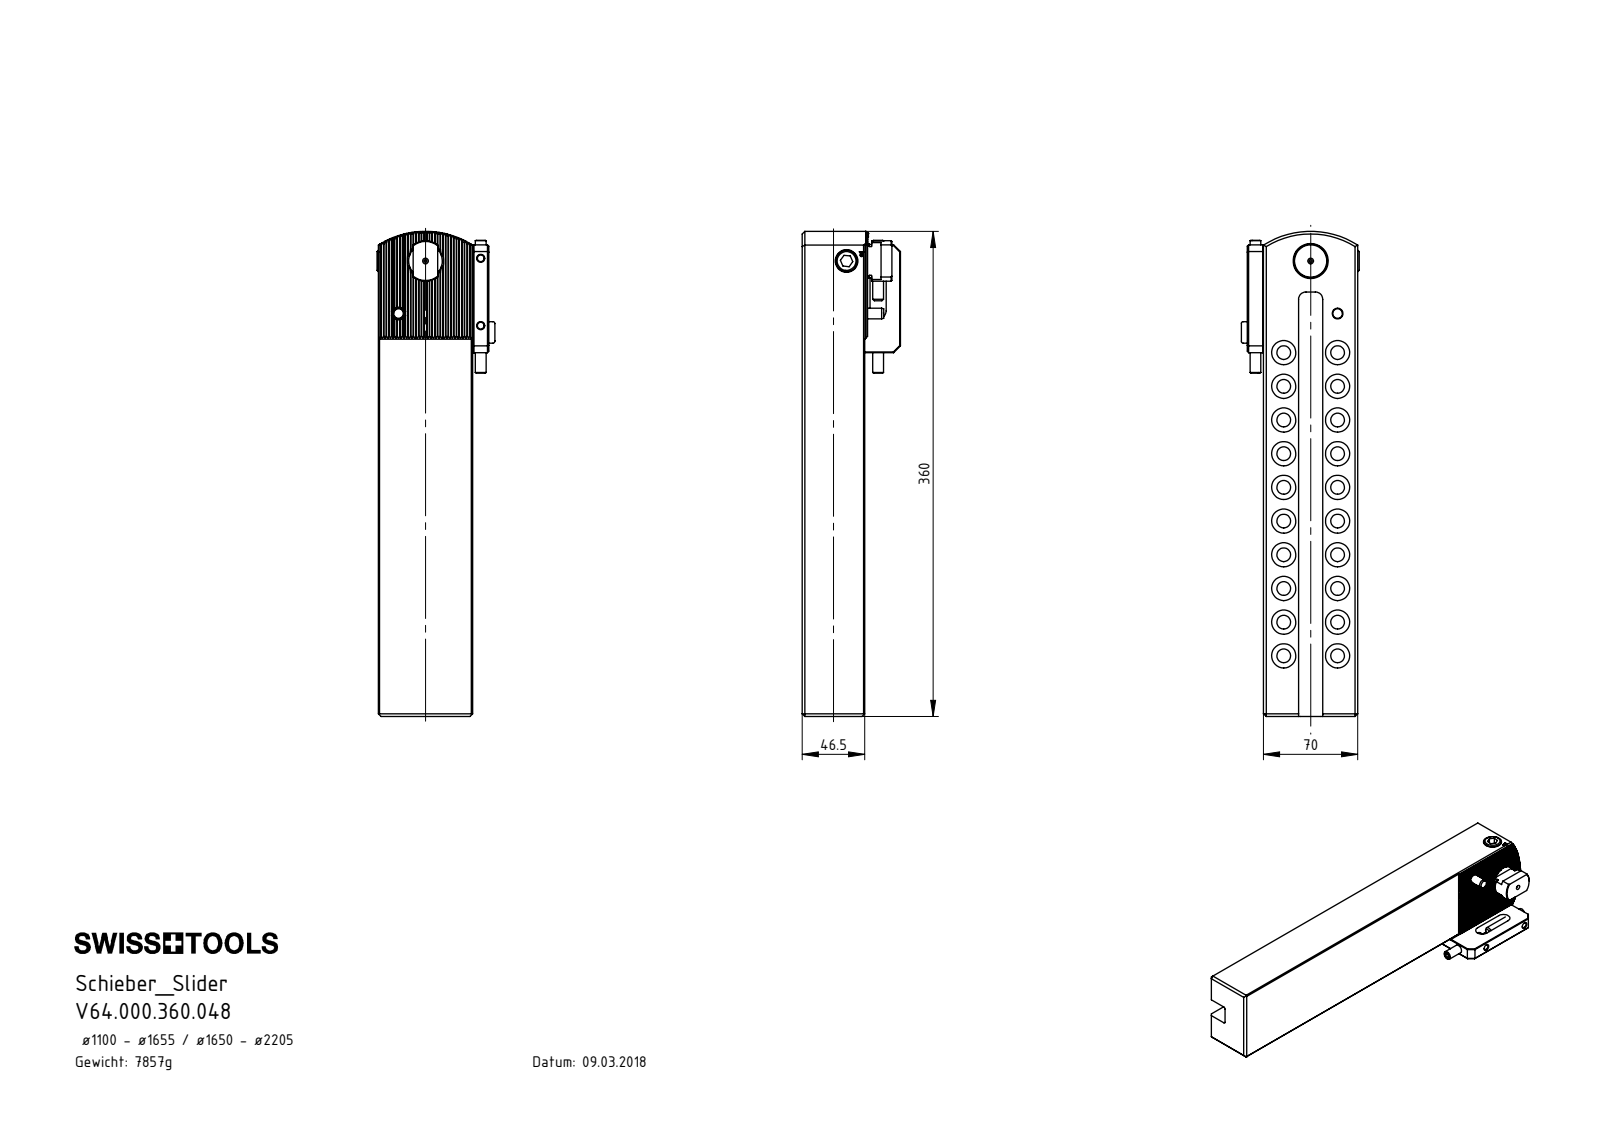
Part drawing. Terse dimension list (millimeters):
name: VK1-ER3.001.028_A; VK3.VK1.360.048; VK3-VK1.360.048_B; VK1-ER2.001.044_A (+6 more)
written by: SolidWorks 2017 (AUTOMOTIVE_DESIGN)
unit: mm
bodies: 10 solids, 543 faces (319 planar, 130 cylindrical, 94 other)
size: 360 × 87.5 × 73
volume: 1 001 000 mm³; area: 162 838 mm²
holes: 21× ⌀18, 20× ⌀10.2, 2× ⌀5, 2× ⌀6, 2× ⌀6.8, 1× ⌀2, 1× ⌀8, 1× ⌀8.5, 1× ⌀10.5, 1× ⌀11, 1× ⌀14, 1× ⌀25
bosses: 2× ⌀16, 1× ⌀10, 1× ⌀8
rounds: 33× R0.14, 4× R2, 3× R1.5, 2× R5.5, 2× R6, 1× R12.3, 1× R15, 1× R65
face distances: 70, 46.5, 44, 26, 26.5, 18, 20, 6.5, 40, 13.5
hole spacings: 25, 47.17, 50, 64.03, 75, 85, 100, 107.7
